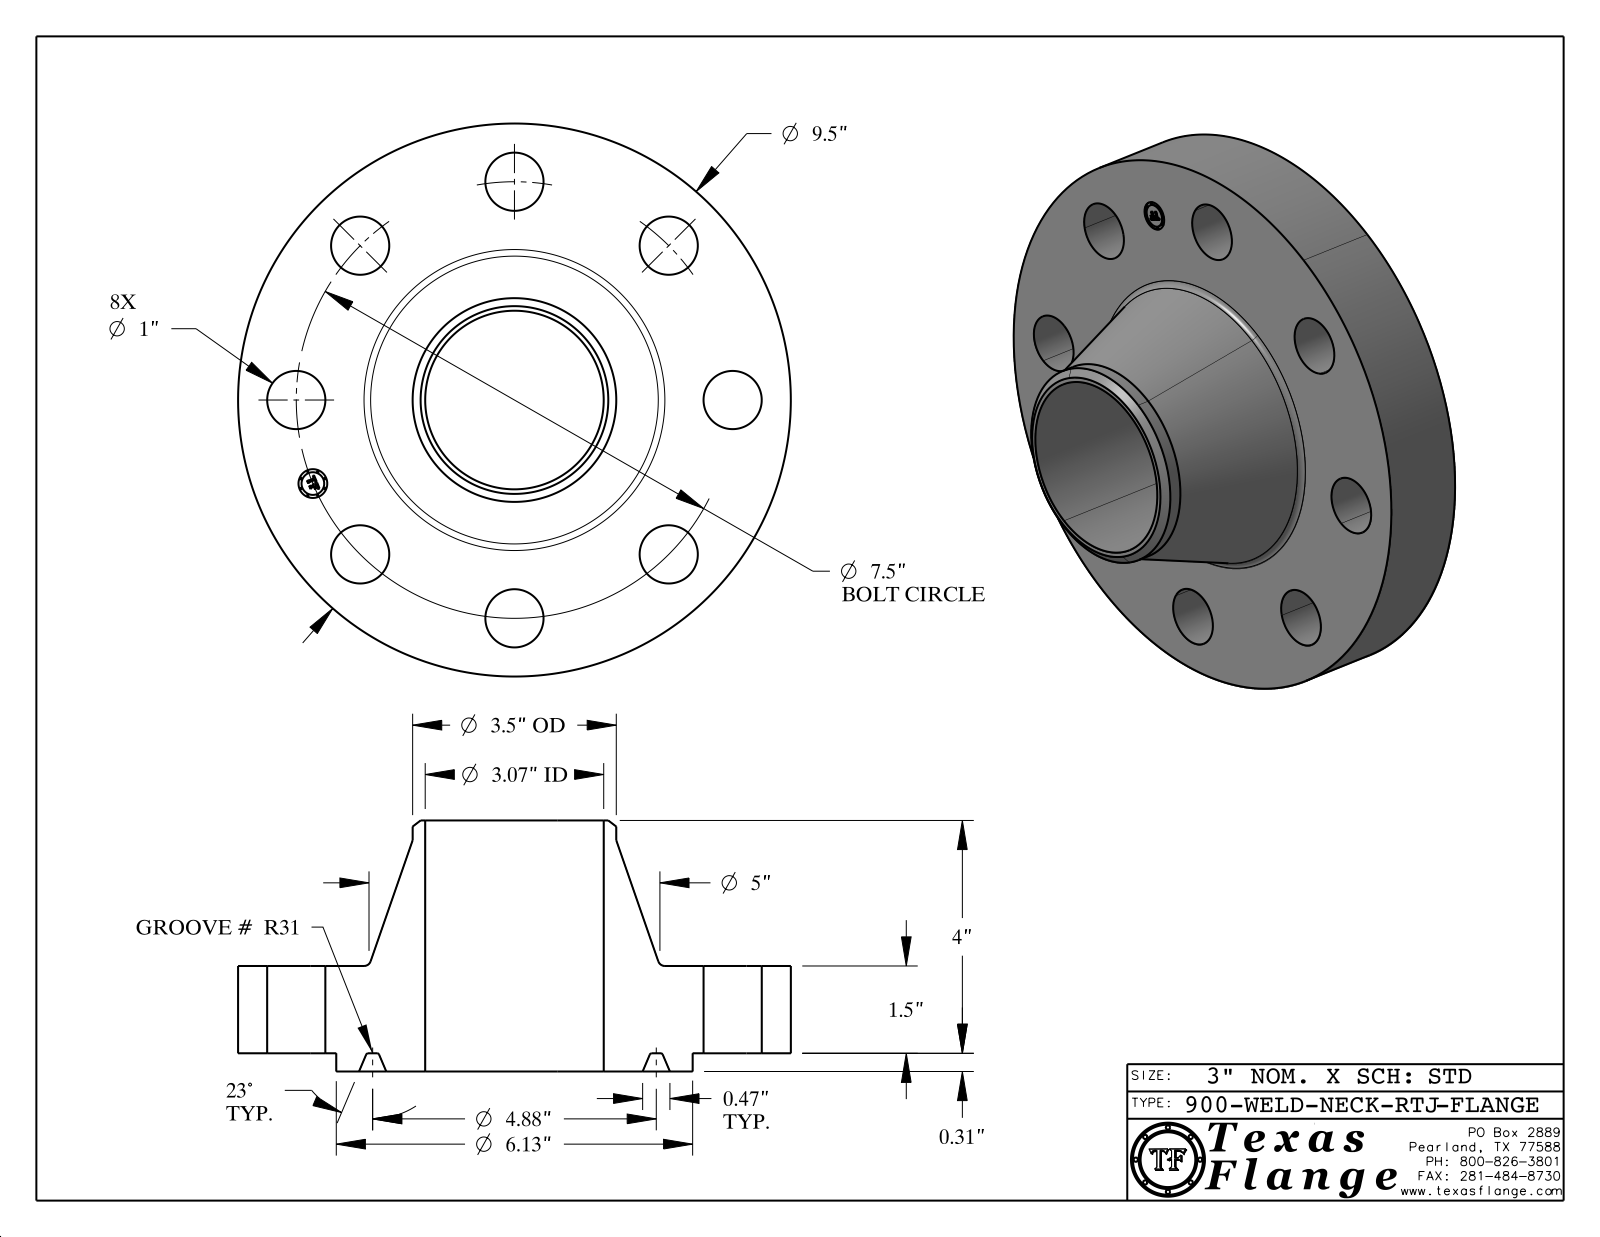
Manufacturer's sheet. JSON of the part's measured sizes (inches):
{"part_name": "900-WELD-NECK-RTJ", "step_written_by": "CATIA V5 STEP AP214 (AUTOMOTIVE_DESIGN)", "units": "inches", "bodies": {"solids": 1, "faces": 429, "planar": 371, "cylindrical": 44, "other": 14}, "overall_size": [9.5, 9.5, 4.313], "volume_in3": 106.8, "surface_area_in2": 273.9, "round_holes": [[1, 8], [0.495, 1], [3.068, 1]], "round_bosses_or_shafts": [[0.03, 8], [9.5, 1], [6.125, 1], [3.5, 1], [0.39, 1]], "face_to_face_distances": [1.5, 0.313, 1.813, 4.313, 4, 2.5, 0.015, 1.798, 1.485, 2.515], "hole_center_spacings": [3.75, 2.87, 5.303, 6.929, 1.463, 6.236, 7.356, 7.5]}
